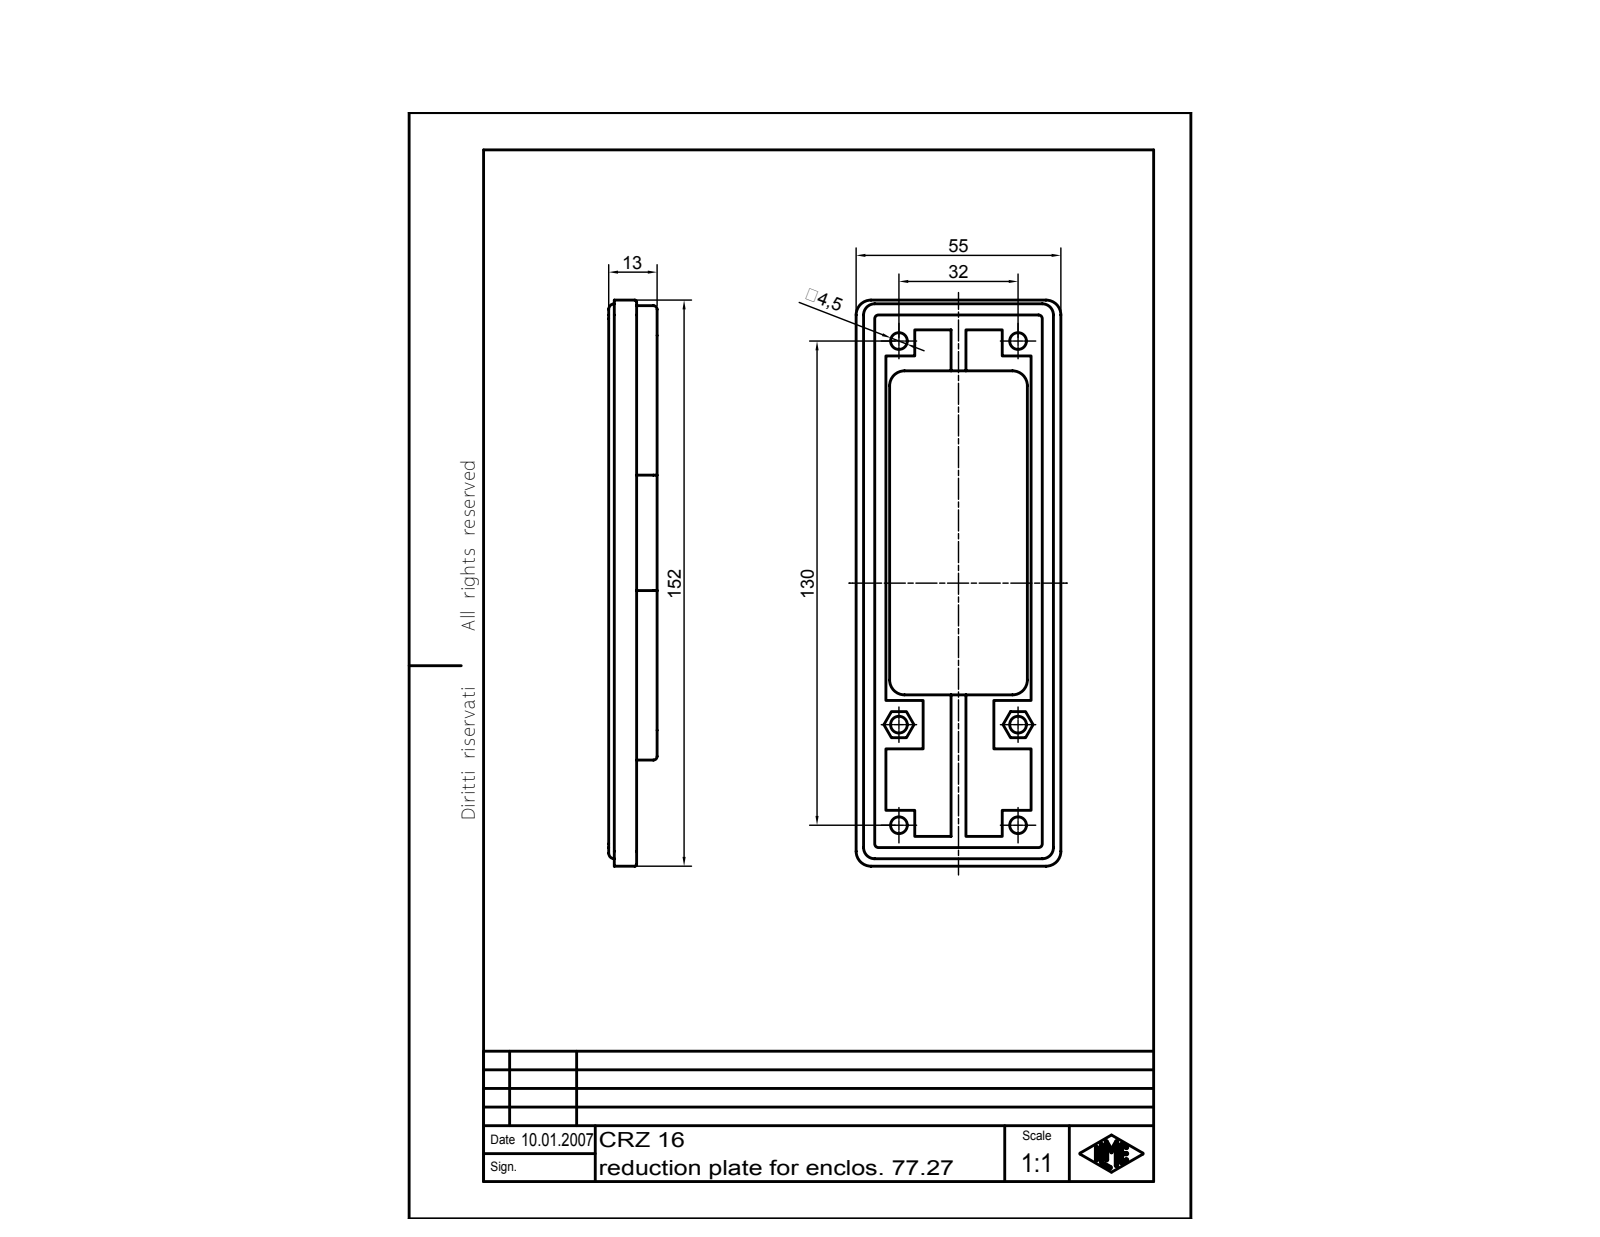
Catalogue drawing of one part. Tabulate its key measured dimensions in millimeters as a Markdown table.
| quantity | value |
| --- | --- |
| part name | CRZ 16 |
| STEP written by | Autodesk Inventor 7 (AUTOMOTIVE_DESIGN) |
| units | millimeters |
| bodies | 1 solid, 209 faces (107 planar, 82 cylindrical, 20 other) |
| overall size | 152 × 55 × 13 |
| volume | 31 885 mm³ |
| surface area | 18 873 mm² |
| round holes (diameter × count) | 4.5 × 6 |
| partial cylindrical surfaces (radius × count) | 0.1 × 14, 1 × 8, 4 × 8, 0.5 × 4, 1.5 × 4, 5 × 4, 8 × 4 |
| main face-to-face distances | 3, 6, 1.75, 4.75, 50.25, 53.25, 55, 8, 48.5, 47 |
| hole center spacings | 32, 27, 41.87, 103, 107.86, 130, 133.88 |
